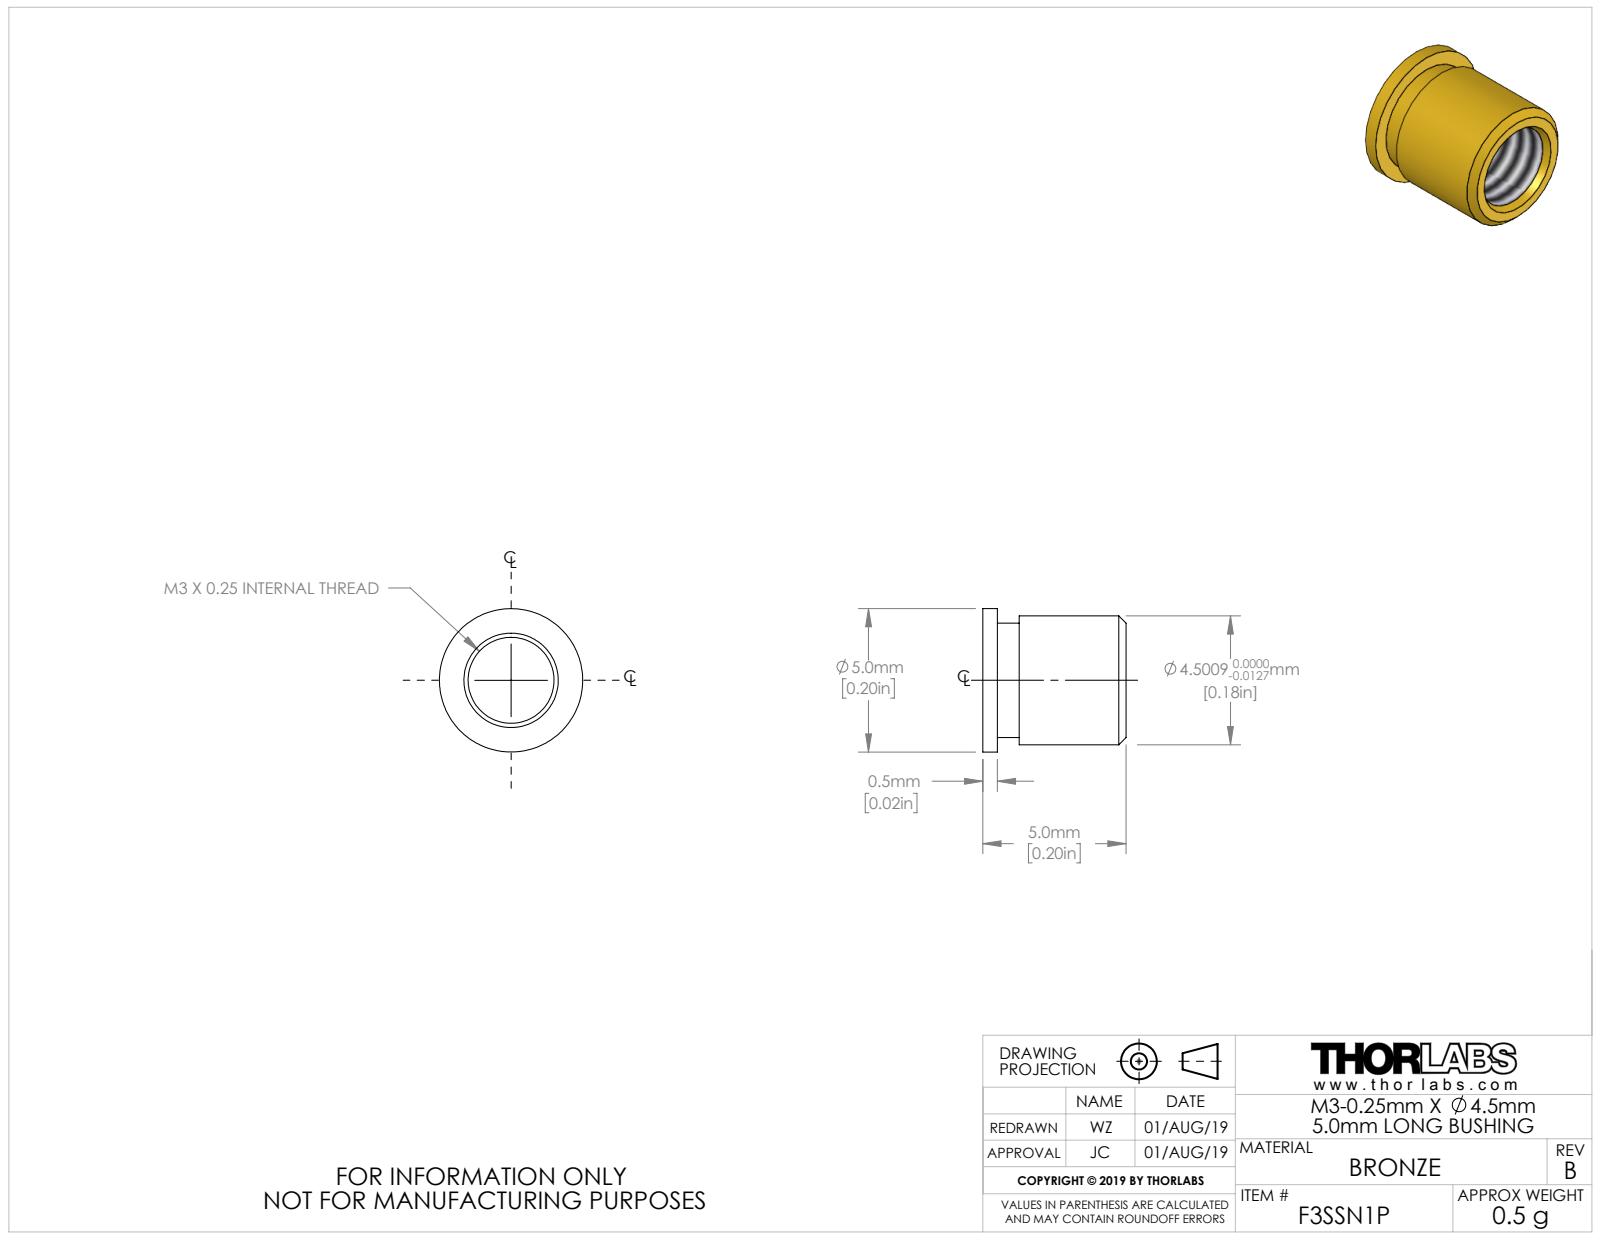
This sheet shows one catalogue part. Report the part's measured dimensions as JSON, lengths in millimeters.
{"part_name": "18997-E0W", "step_written_by": "SolidWorks 2007 (AUTOMOTIVE_DESIGN)", "units": "millimeters", "bodies": {"solids": 1, "faces": 18, "planar": 4, "cylindrical": 8, "other": 6}, "overall_size": [5, 5, 5], "volume_mm3": 43, "surface_area_mm2": 145, "round_holes": [[3, 1]], "round_bosses_or_shafts": [[5, 1], [4.5, 1], [3.99, 1]], "face_to_face_distances": [0.51, 5, 4.49, 1.27, 0.76, 3.73]}
